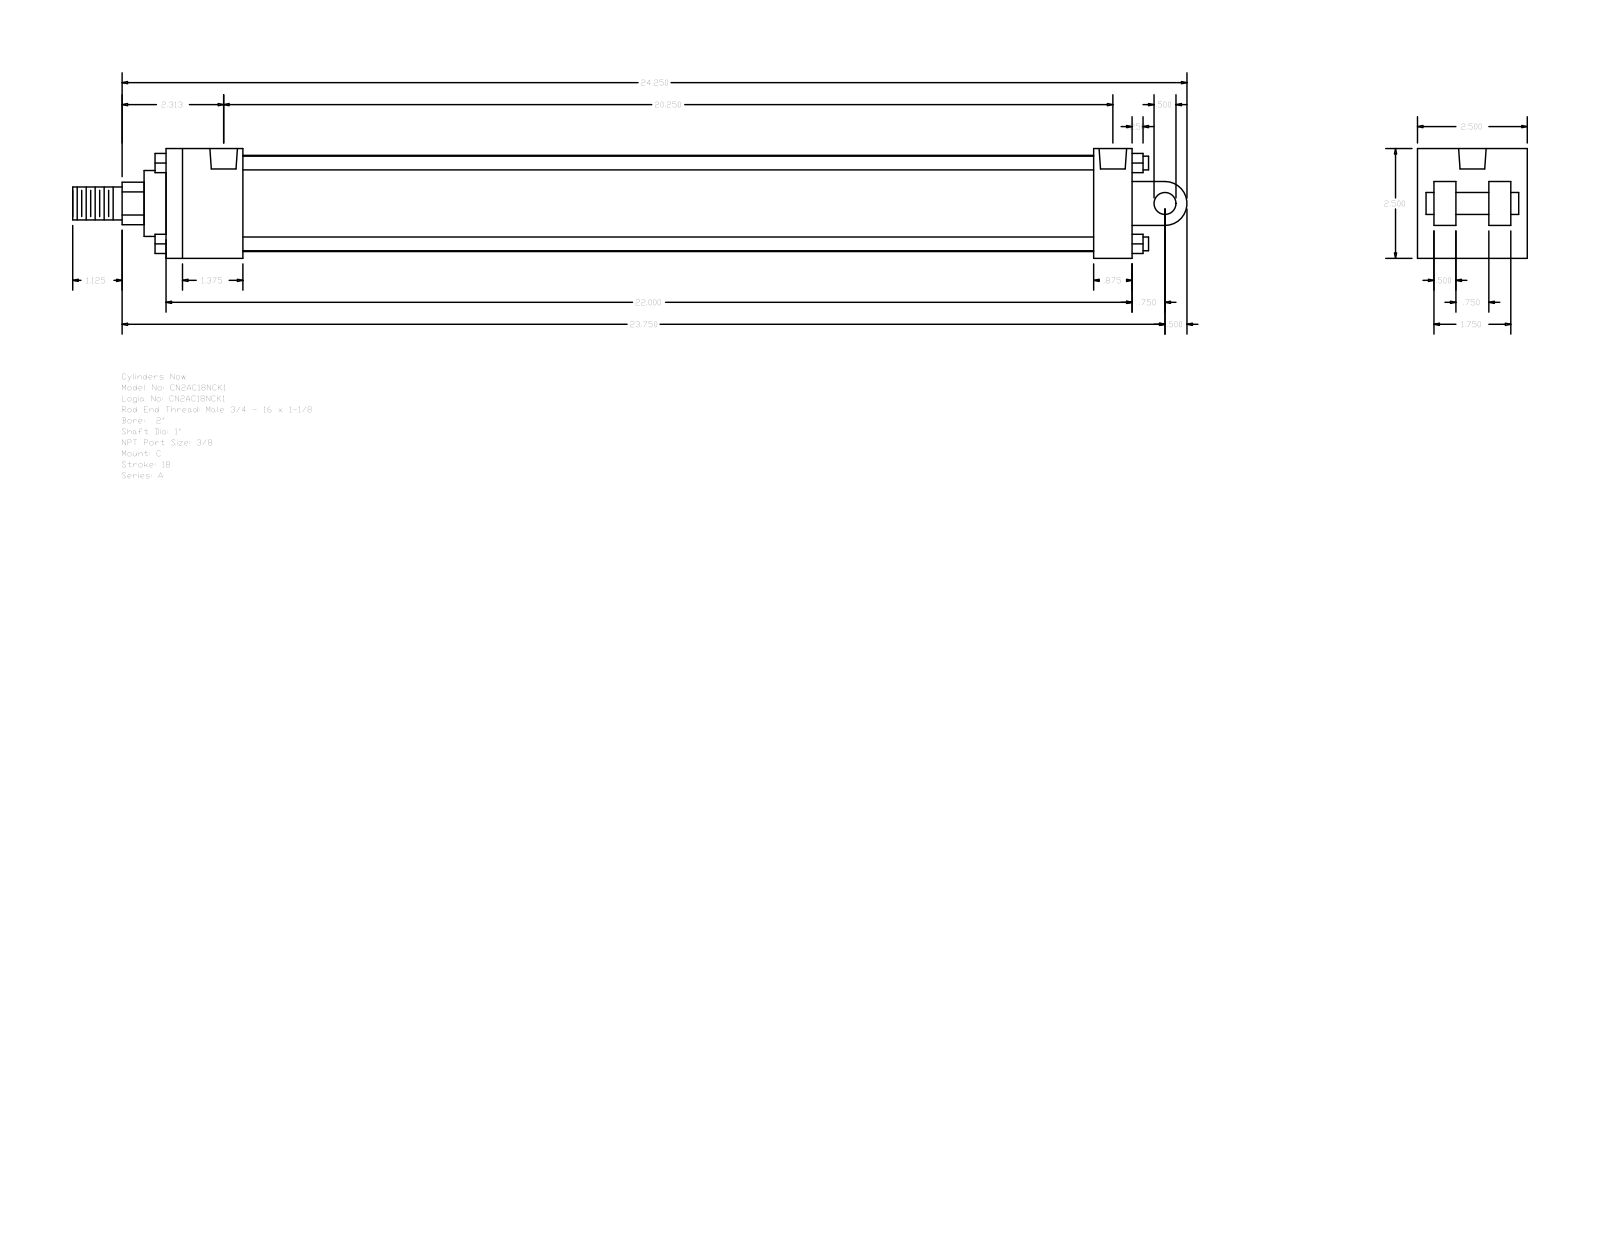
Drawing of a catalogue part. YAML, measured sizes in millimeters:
part_name: "A_C__0200_1"
step_written_by: "GSSL Pune (CONFIG_CONTROL_DESIGN)"
units: millimeters
bodies: {solids: 0, faces: 135, planar: 102, cylindrical: 33, other: 0}
overall_size: [644.52, 63.5, 63.5]
round_holes:
  - {diameter: 5.56, count: 4}
  - {diameter: 15.93, count: 2}
round_bosses_or_shafts:
  - {diameter: 7.94, count: 4}
  - {diameter: 55.63, count: 1}
  - {diameter: 38.1, count: 1}
  - {diameter: 25.4, count: 1}
  - {diameter: 19.05, count: 1}
  - {diameter: 12.7, count: 1}
partial_cylinders:
  - {radius: 12.29, count: 1}
  - {radius: 12.7, count: 1}
face_to_face_distances: [63.5, 22.22, 558.8, 44.45, 12.7, 514.35, 536.58, 492.13, 9.52, 53.98]
hole_center_spacings: [508.78, 1.59, 3.98, 510.37, 512.76, 514.35]
